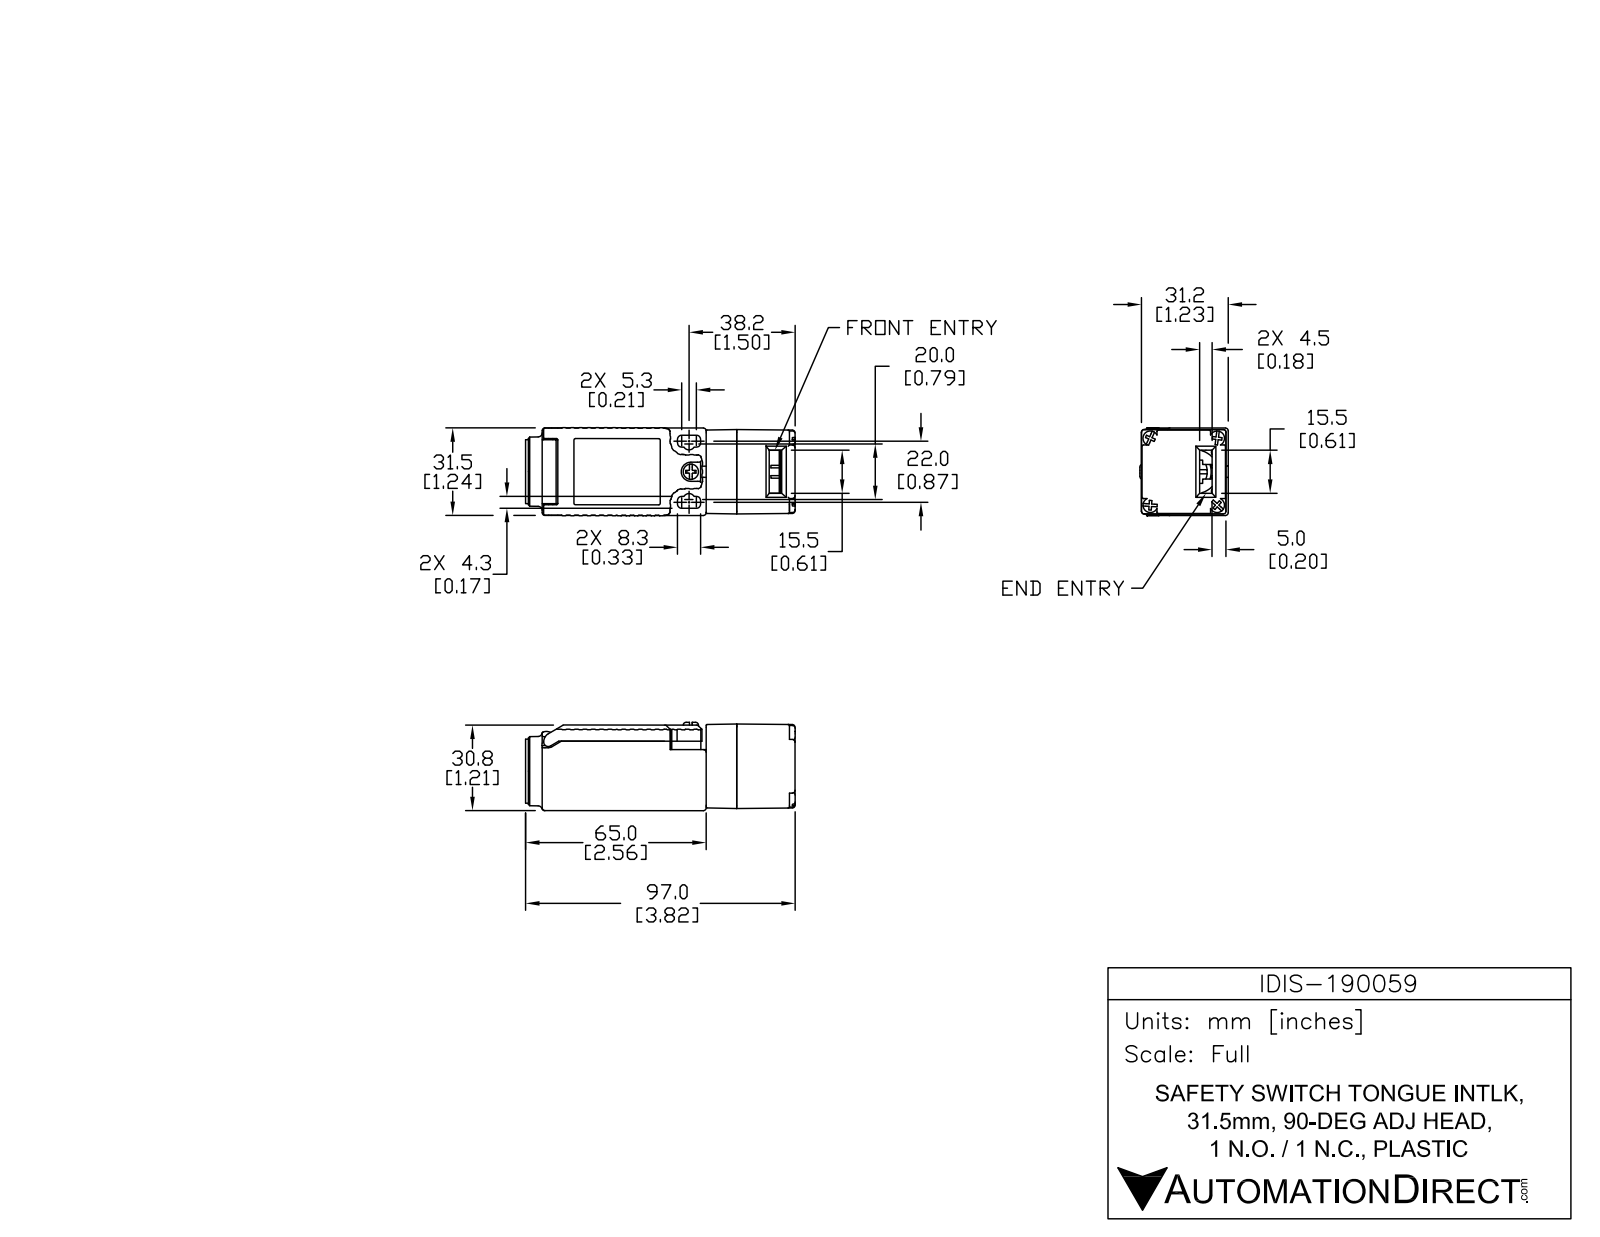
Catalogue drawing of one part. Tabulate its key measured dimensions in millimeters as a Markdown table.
| quantity | value |
| --- | --- |
| part name | IDIS-190059 |
| STEP written by | SolidWorks 2013 (AUTOMOTIVE_DESIGN) |
| units | millimeters |
| bodies | 1 solid, 475 faces (228 planar, 170 cylindrical, 77 other) |
| overall size | 103 × 32.2 × 31.5 |
| volume | 84 450 mm³ |
| surface area | 19 432 mm² |
| round holes (diameter × count) | 4 × 2, 16.19 × 1, 18.5 × 1, 21.2 × 1 |
| round bosses / shafts (diameter × count) | 5 × 5, 25 × 1, 23 × 1, 17.19 × 1 |
| partial cylindrical surfaces (radius × count) | 0.5 × 27, 1 × 21, 0.25 × 20, 1.5 × 8, 2.4 × 6, 3 × 4, 0.42 × 2, 2 × 2 |
| main face-to-face distances | 31.5, 0.5, 30.2, 1, 30.37, 30.36, 5, 2.5, 29.99, 5.6 |
| hole center spacings | 22 |
